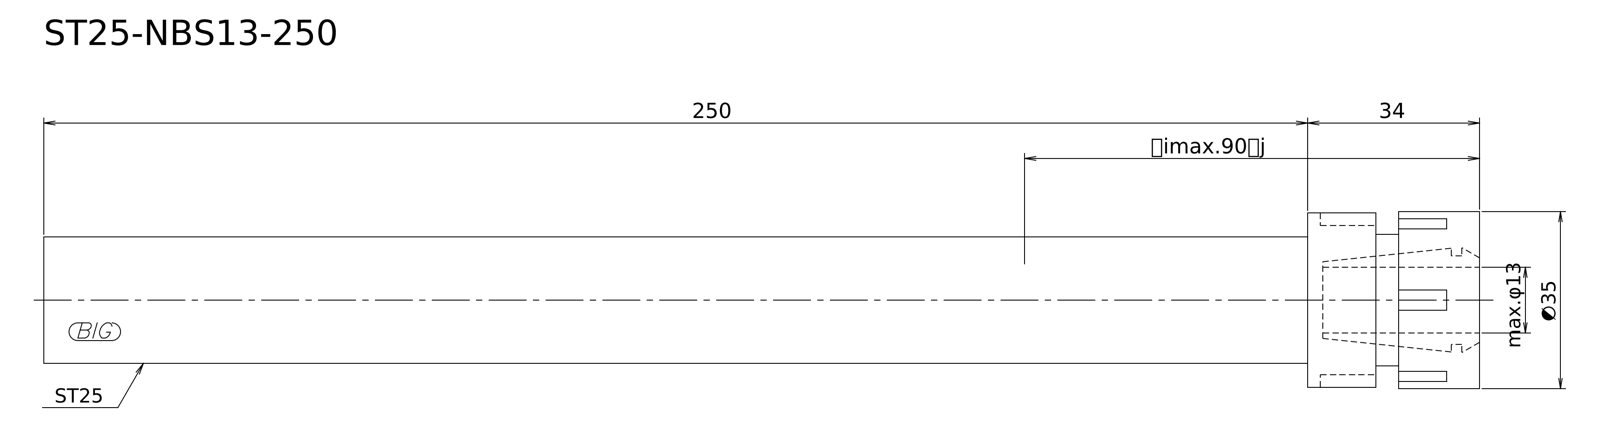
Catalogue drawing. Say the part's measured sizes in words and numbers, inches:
Its 3-D file was written by "Kubotek KeyCreator V8.5.1 (14335) (CONFIG_CONTROL_DESIGN)". It is 1 solid with 9 faces: 5 planar, 4 cylindrical and 0 other. Overall it measures 11.181 by 1.378 by 1.378 inches. Its volume is 9.344 cubic inches and its surface area 40.23 square inches. Round bosses or shafts: 1 of diameter 1.378, 1 of diameter 1.358, 1 of diameter 1.024, 1 of diameter 0.984. The main face-to-face distances are 11.181, 1.339, 9.843, 0.63, 0.709, 10.551, 0.807, 0.177, 0.531, 10.374.
